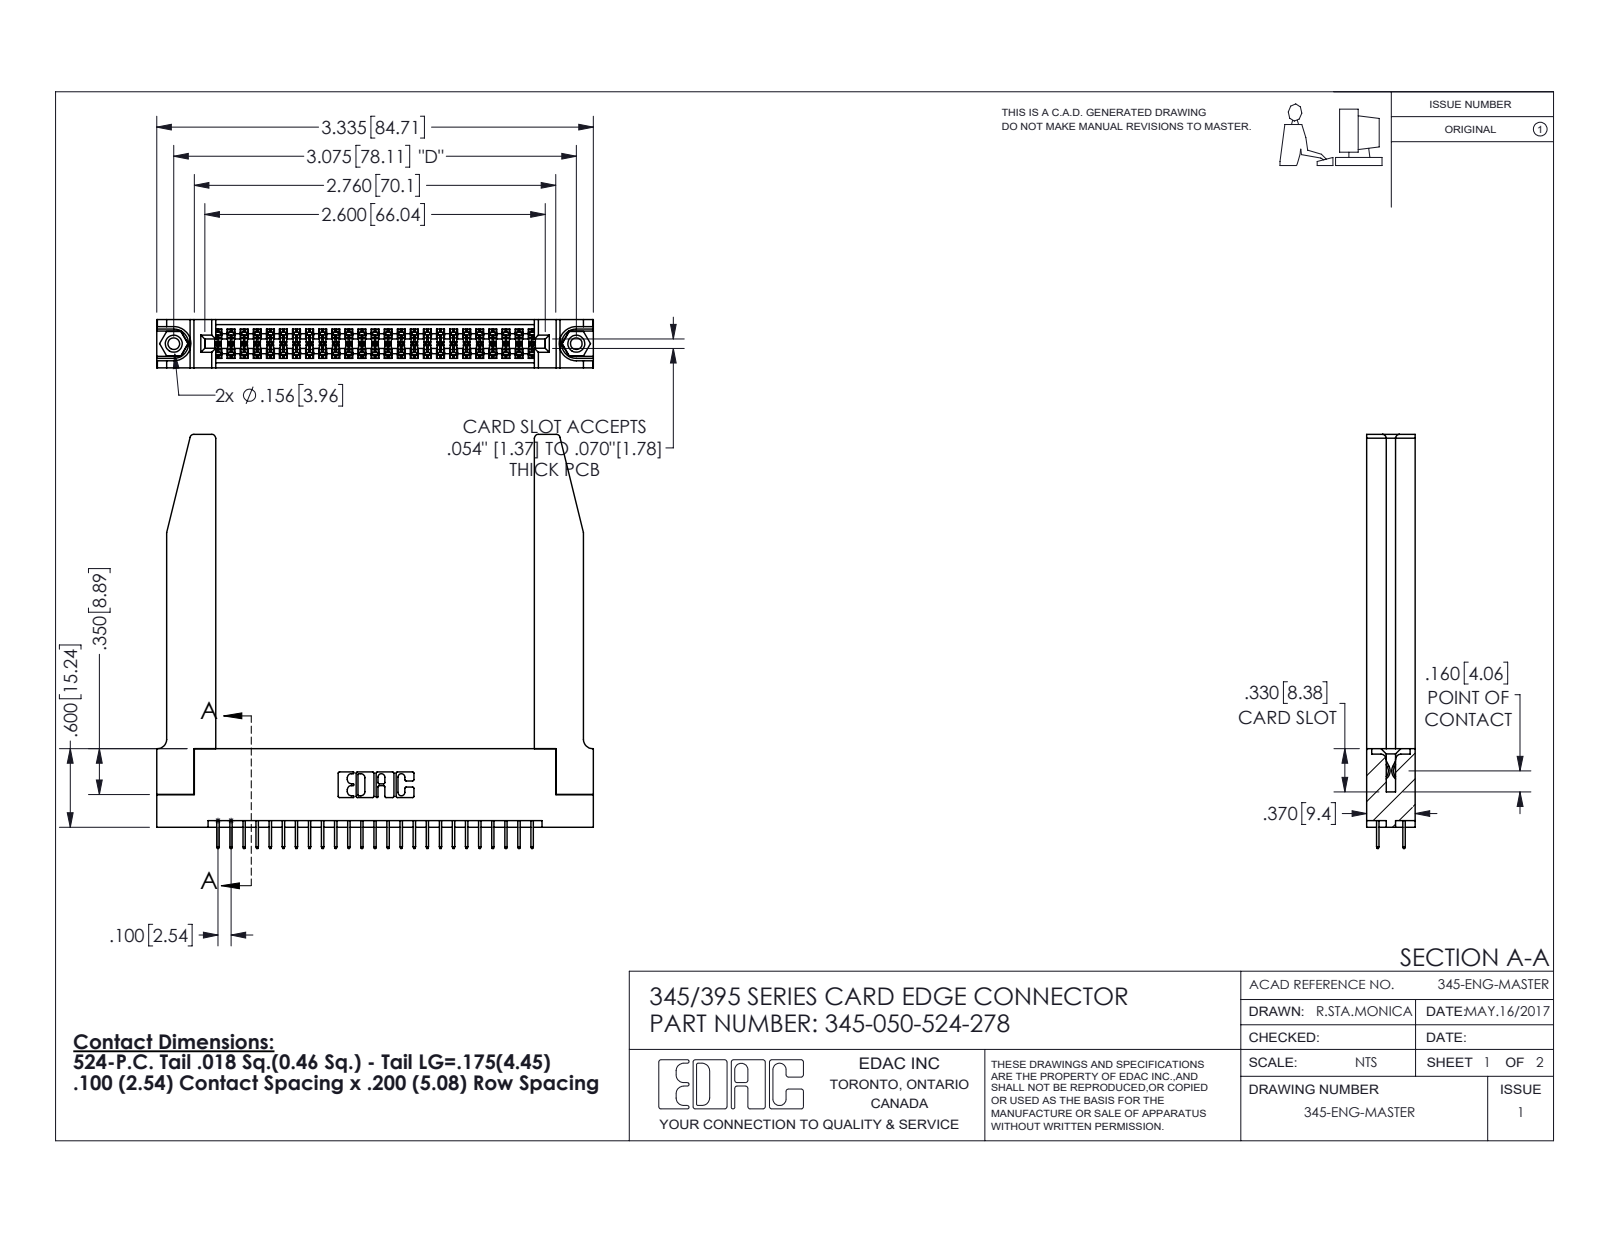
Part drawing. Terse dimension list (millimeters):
name: 345-292-001_345-293-124; 345 Part_Flush Mounting Lugs - 0.156 Dia-TH; 345-050-524-278; 345-220-078_345-220-078 (+1 more)
written by: SolidWorks 2016 (CONFIG_CONTROL_DESIGN)
unit: mm
bodies: 55 solids, 3060 faces (2172 planar, 836 cylindrical, 52 other)
size: 84.7 × 80.3 × 9.4
volume: 15 800 mm³; area: 18 130 mm²
holes: 2× ⌀2.3, 2× ⌀3.2, 2× ⌀4, 1× ⌀1.6
bosses: 2× ⌀3.9
rounds: 75× R0.2, 22× R0.3, 8× R0.8, 6× R0.2, 6× R0.8, 3× R0.7, 2× R0.4, 2× R0.5
face distances: 9.4, 1.8, 7.6, 5.1, 2.5, 6.9, 0.6, 5.7, 3.8, 3.8
hole spacings: 6.9, 72.1, 78.1
